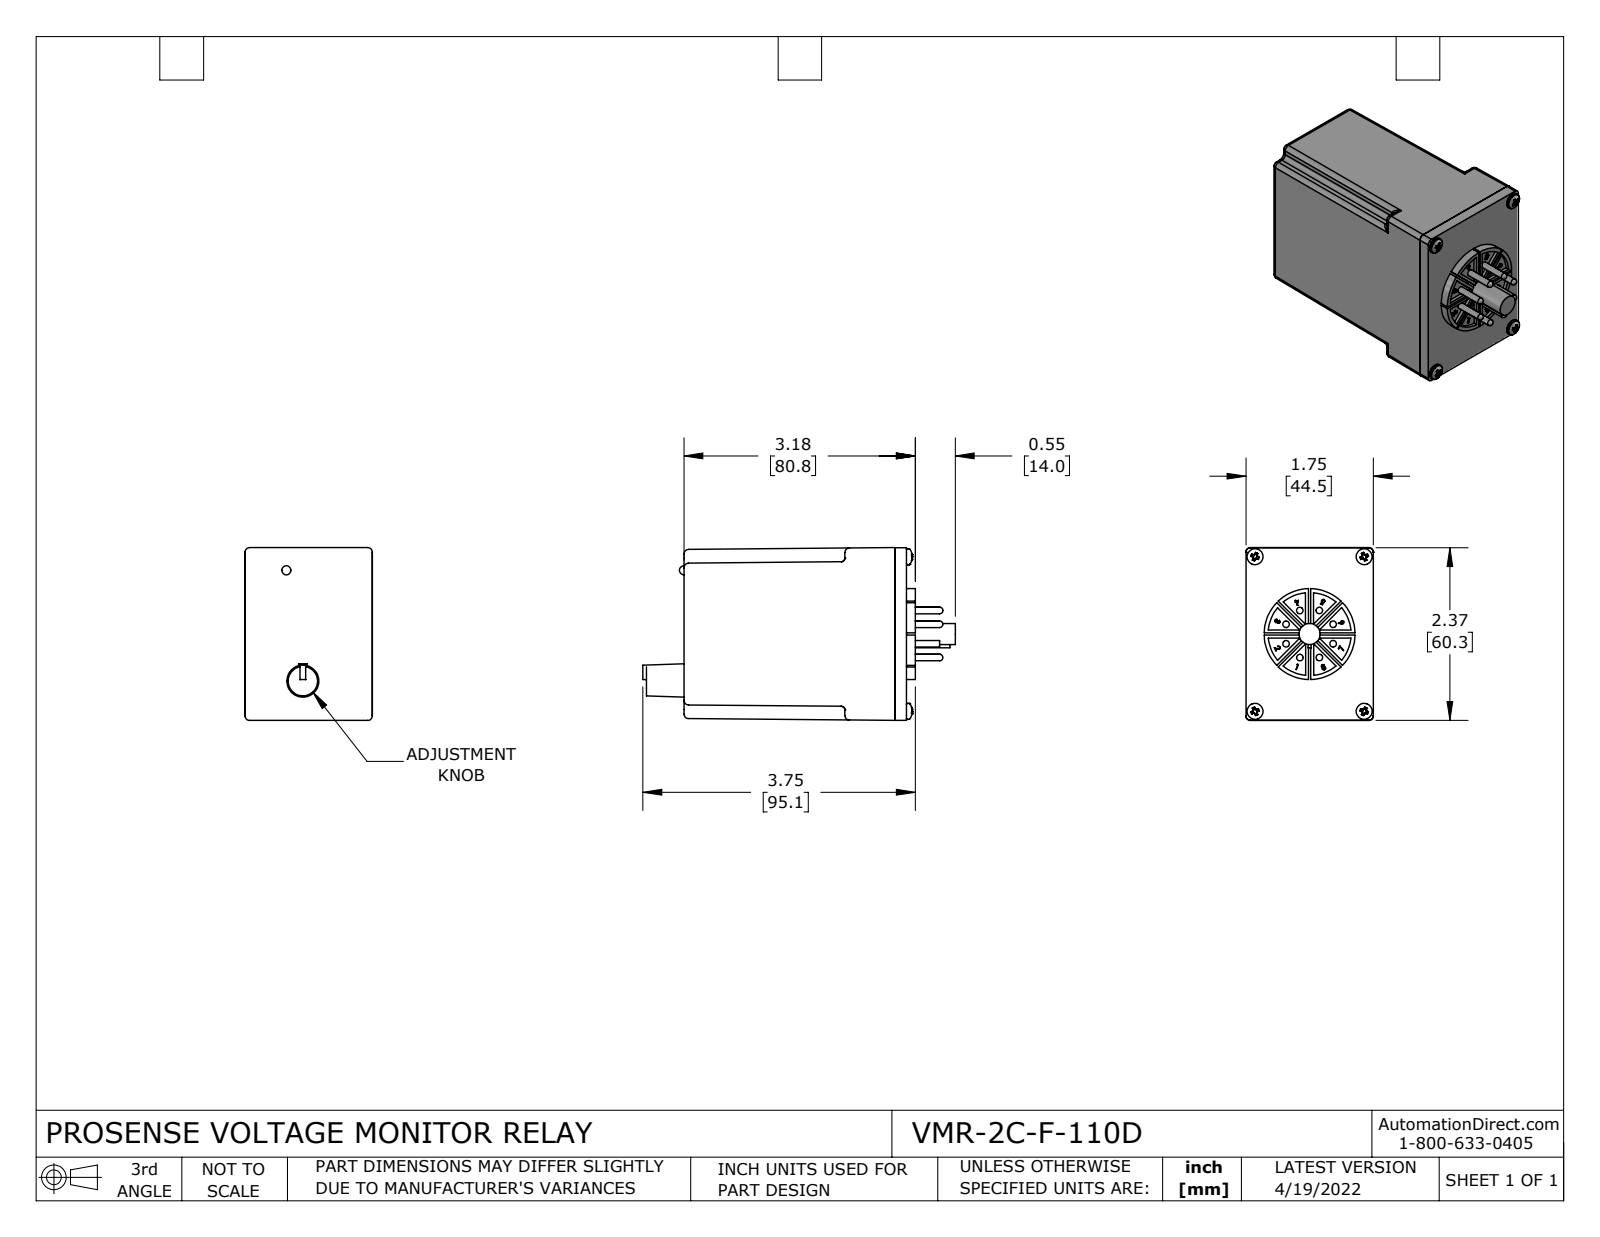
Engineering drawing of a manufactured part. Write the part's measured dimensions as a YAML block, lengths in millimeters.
part_name: "VMR-2C-F-110D"
step_written_by: "SolidWorks 2021 (CONFIG_CONTROL_DESIGN)"
units: millimeters
bodies: {solids: 17, faces: 542, planar: 221, cylindrical: 164, other: 157}
overall_size: [109.1, 60.3, 44.5]
volume: 202100
surface_area: 29540
round_holes:
  - {diameter: 3.2, count: 4}
round_bosses_or_shafts:
  - {diameter: 2.3, count: 8}
  - {diameter: 5.6, count: 4}
  - {diameter: 31.8, count: 1}
  - {diameter: 7.4, count: 1}
partial_cylinders:
  - {radius: 1.6, count: 32}
  - {radius: 0.1, count: 8}
  - {radius: 1.3, count: 4}
  - {radius: 14.5, count: 1}
face_to_face_distances: [73.7, 4.1, 77.7, 1.8, 5.8, 79.5, 4.8, 1.3, 3, 7.1]
hole_center_spacings: [38.1, 54, 66.1]
